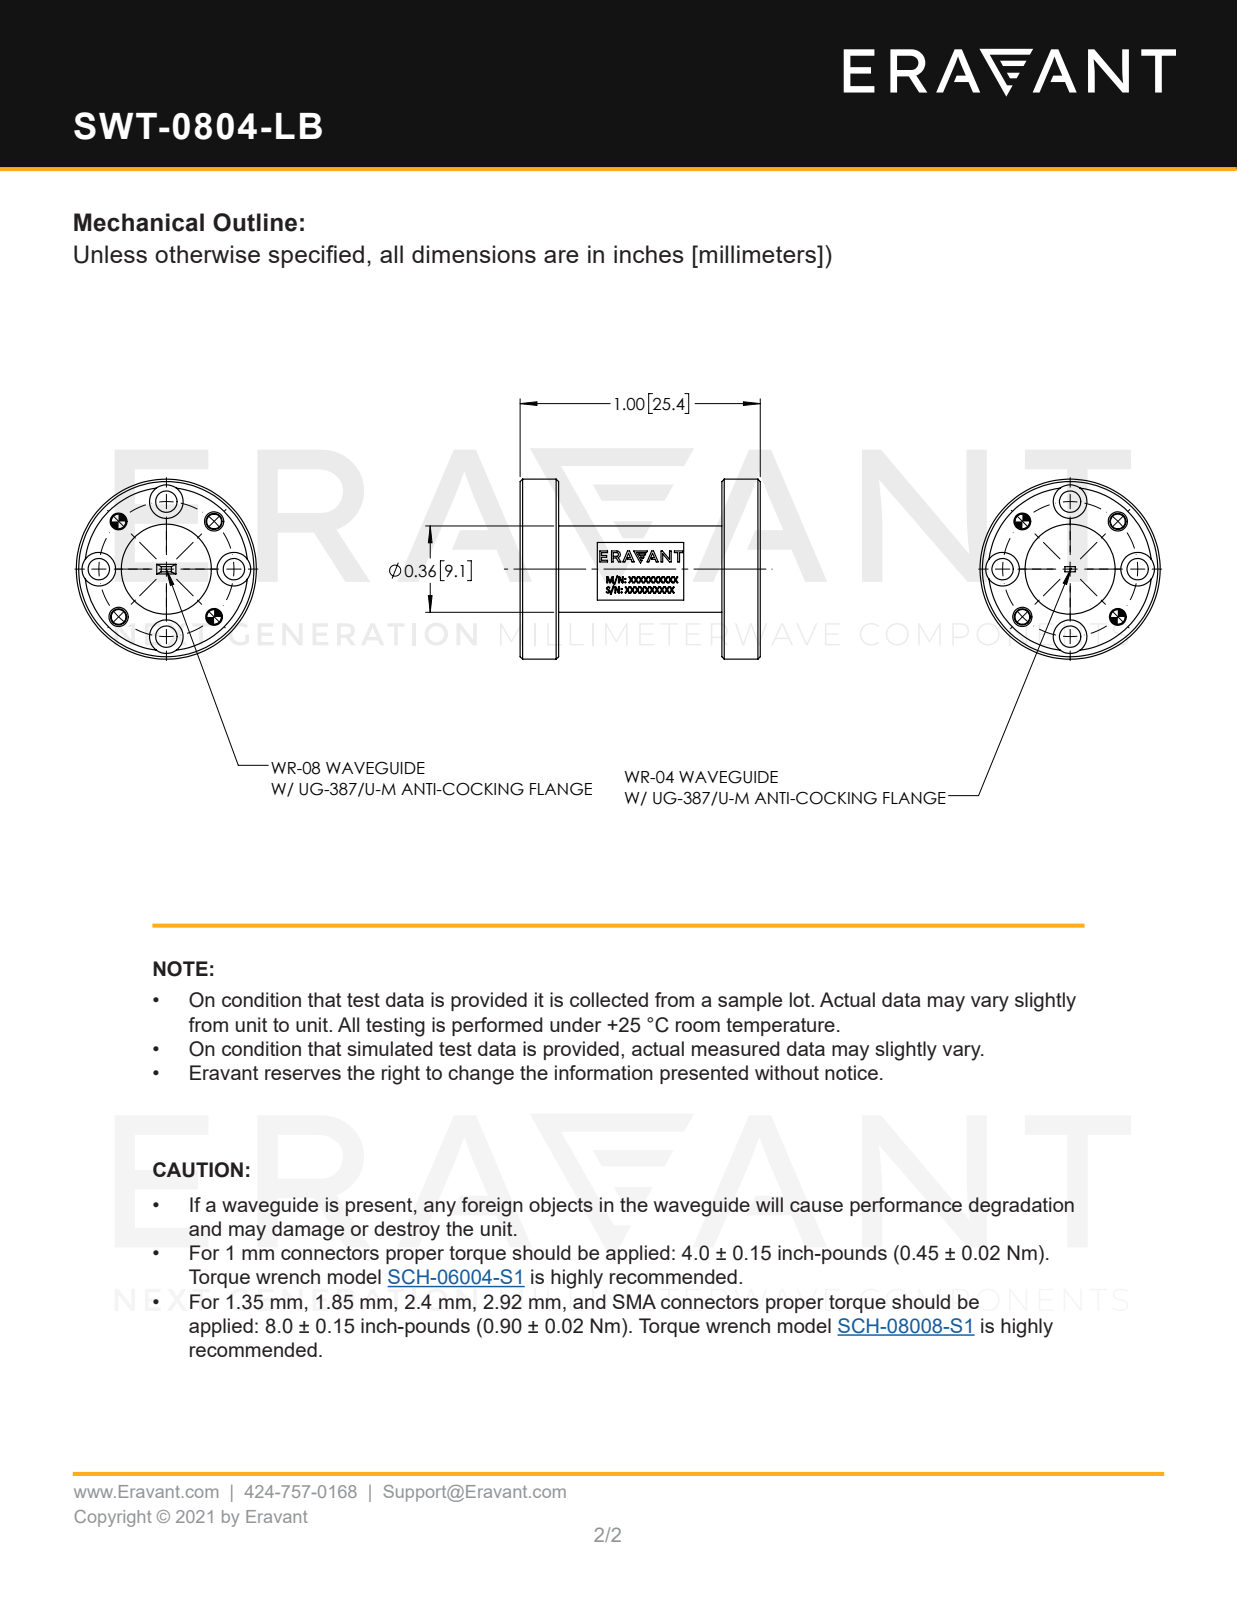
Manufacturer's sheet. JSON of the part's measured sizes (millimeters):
{"part_name": "SWT-0804-LB", "step_written_by": "SolidWorks 2021 (CONFIG_CONTROL_DESIGN)", "units": "millimeters", "bodies": {"solids": 5, "faces": 148, "planar": 34, "cylindrical": 74, "other": 40}, "overall_size": [33.1, 19.1, 19.1], "volume_mm3": 3110, "surface_area_mm2": 2494, "round_holes": [[1.5, 4], [1.7, 4], [2.3, 4], [3.6, 4], [17.3, 1]], "round_bosses_or_shafts": [[1.6, 4], [19.1, 1], [9.5, 1], [9.1, 1]], "face_to_face_distances": [3.6, 20.8, 0.5, 4.1, 21.3, 24.9, 17.3, 24.4, 25.4, 1.5], "hole_center_spacings": [5.5, 7.1, 10.1, 13.2, 14.3]}
